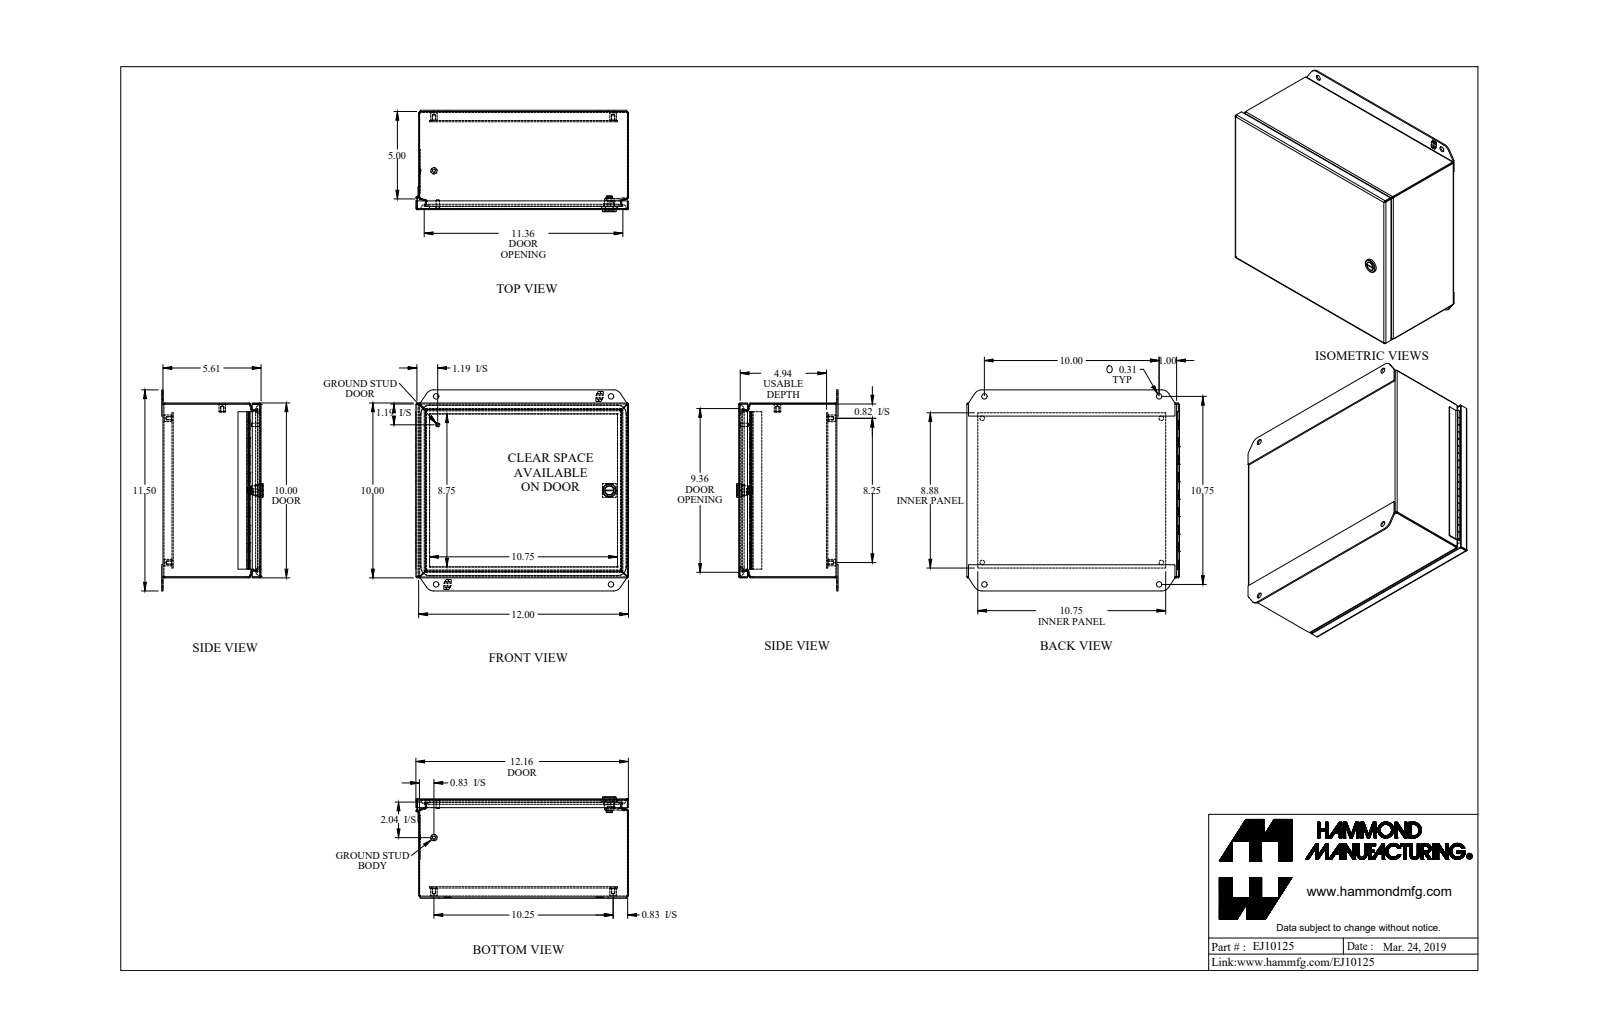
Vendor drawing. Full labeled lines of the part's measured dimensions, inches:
Part name (STEP PRODUCT): EJ10125_Default
STEP written by: SolidWorks 2019 (CONFIG_CONTROL_DESIGN)
Units: inches
Bodies: 16 solids, 675 faces (377 planar, 206 cylindrical, 92 other)
Overall size (bounding box): 12.165 × 11.5 × 5.805
Volume: 42.92 in³ · Surface area: 1 411 in²
Round holes (diameter × count): ⌀0.156 ×5, ⌀0.265 ×4, ⌀0.313 ×4, ⌀0.05 ×1, ⌀0.516 ×1
Round bosses / shafts (diameter × count): ⌀0.375 ×5, ⌀0.788 ×1, ⌀0.535 ×1, ⌀0.496 ×1, ⌀0.435 ×1, ⌀0.25 ×1, ⌀0.188 ×1, ⌀0.1 ×1
Partial cylindrical surfaces — rounded edges, fillets, slot ends (radius × count): R0.029 ×16, R0.086 ×16, R0.281 ×10, R0.25 ×4, R0.499 ×4, R0.5 ×4, R0.06 ×2, R0.539 ×2
Main face-to-face distances: 0.057, 5.554, 0.072, 0.589, 9.943, 5.611, 5.497, 11.943, 0.46, 0.517
Hole centre spacings: 10.202, 13.158, 13.884, 1.256, 1.257, 4.131, 8.25, 8.25
